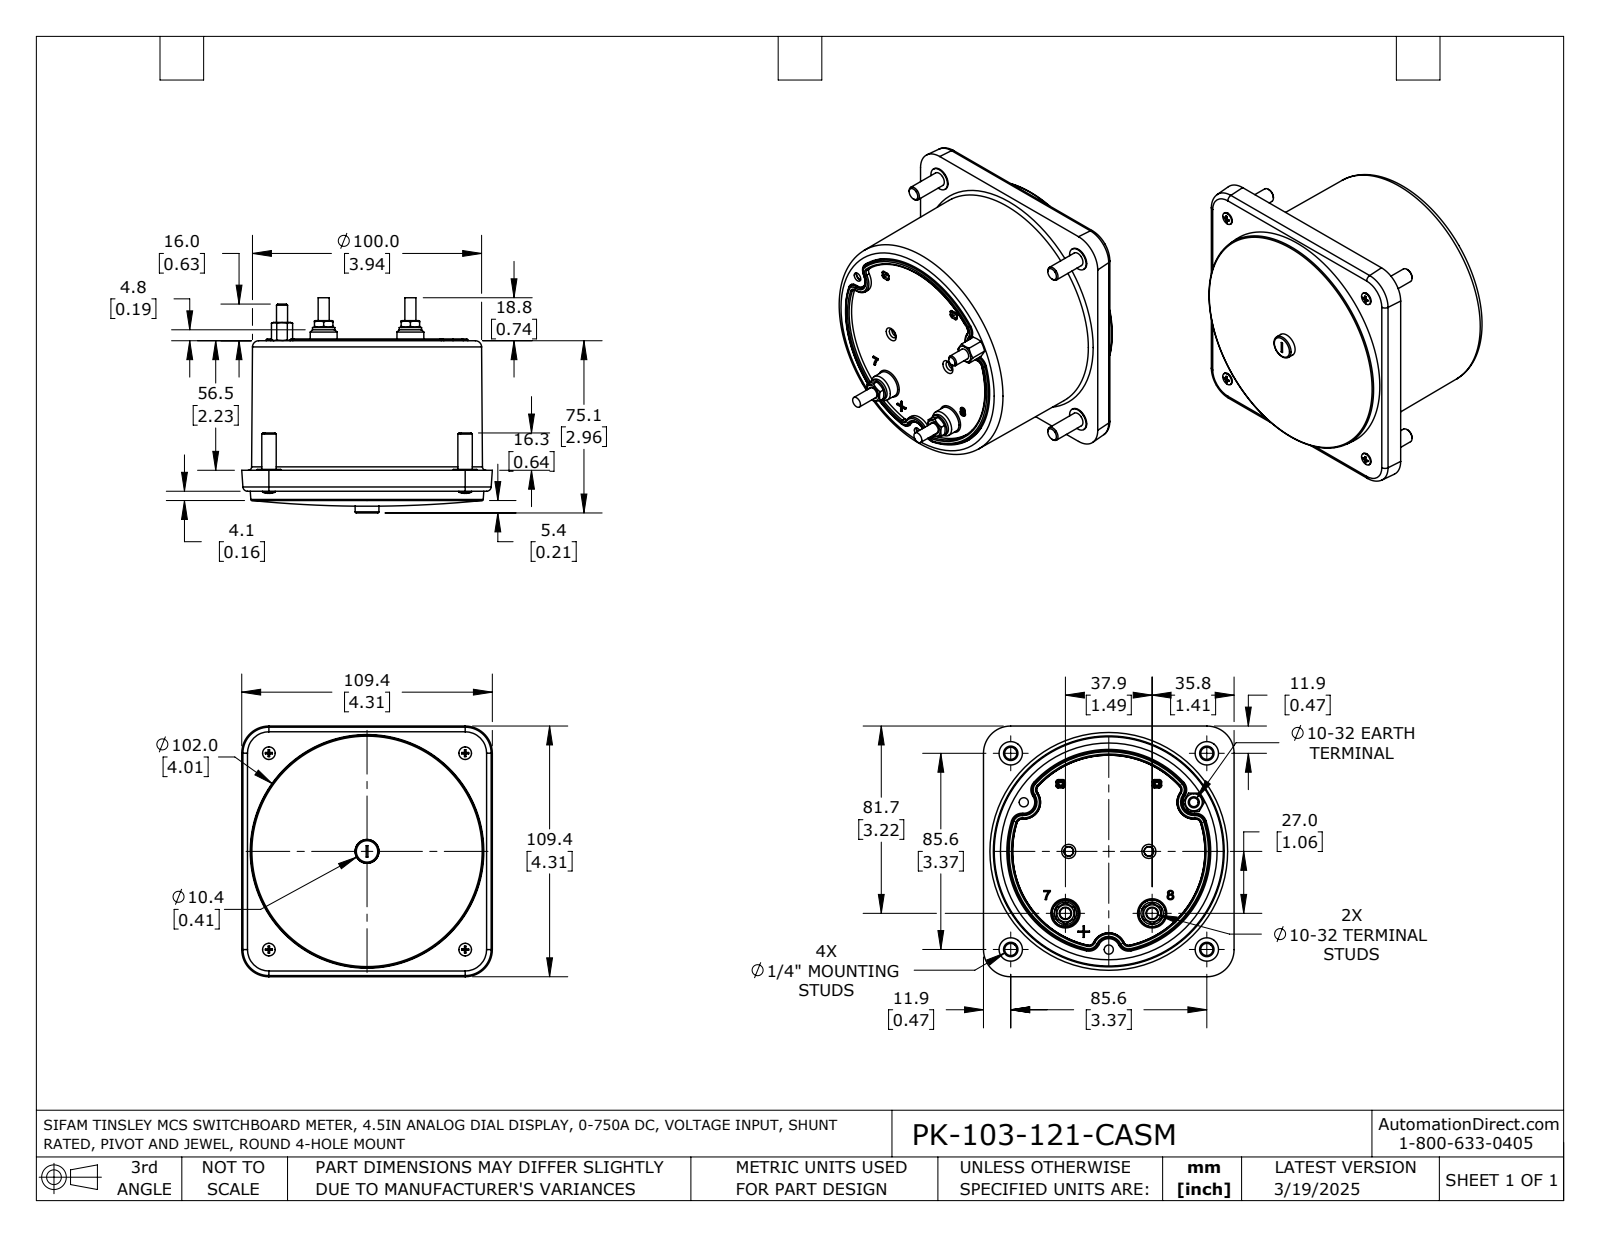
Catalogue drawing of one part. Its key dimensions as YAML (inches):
part_name: "PK-103-121-CASM"
step_written_by: "SolidWorks 2021 (AUTOMOTIVE_DESIGN)"
units: inches
bodies: {solids: 1, faces: 609, planar: 167, cylindrical: 141, other: 301}
overall_size: [4.307, 4.307, 3.697]
volume: 36.28
surface_area: 82.21
round_holes:
  - {diameter: 0.094, count: 4}
  - {diameter: 0.138, count: 4}
  - {diameter: 0.315, count: 4}
  - {diameter: 0.157, count: 3}
  - {diameter: 0.209, count: 2}
round_bosses_or_shafts:
  - {diameter: 0.402, count: 4}
  - {diameter: 0.248, count: 4}
  - {diameter: 0.217, count: 4}
  - {diameter: 0.114, count: 4}
  - {diameter: 0.19, count: 3}
  - {diameter: 0.384, count: 2}
  - {diameter: 0.146, count: 1}
partial_cylinders:
  - {radius: 0.02, count: 24}
  - {radius: 0.189, count: 9}
  - {radius: 0.079, count: 4}
  - {radius: 1.752, count: 1}
face_to_face_distances: [2.177, 2.537, 0.36, 0.048, 2.225, 2.585, 0.489, 2.715, 2.667, 0.129]
hole_center_spacings: [3.372, 3.37, 3.374, 3.378, 3.38, 4.769, 0.971, 1.126]
